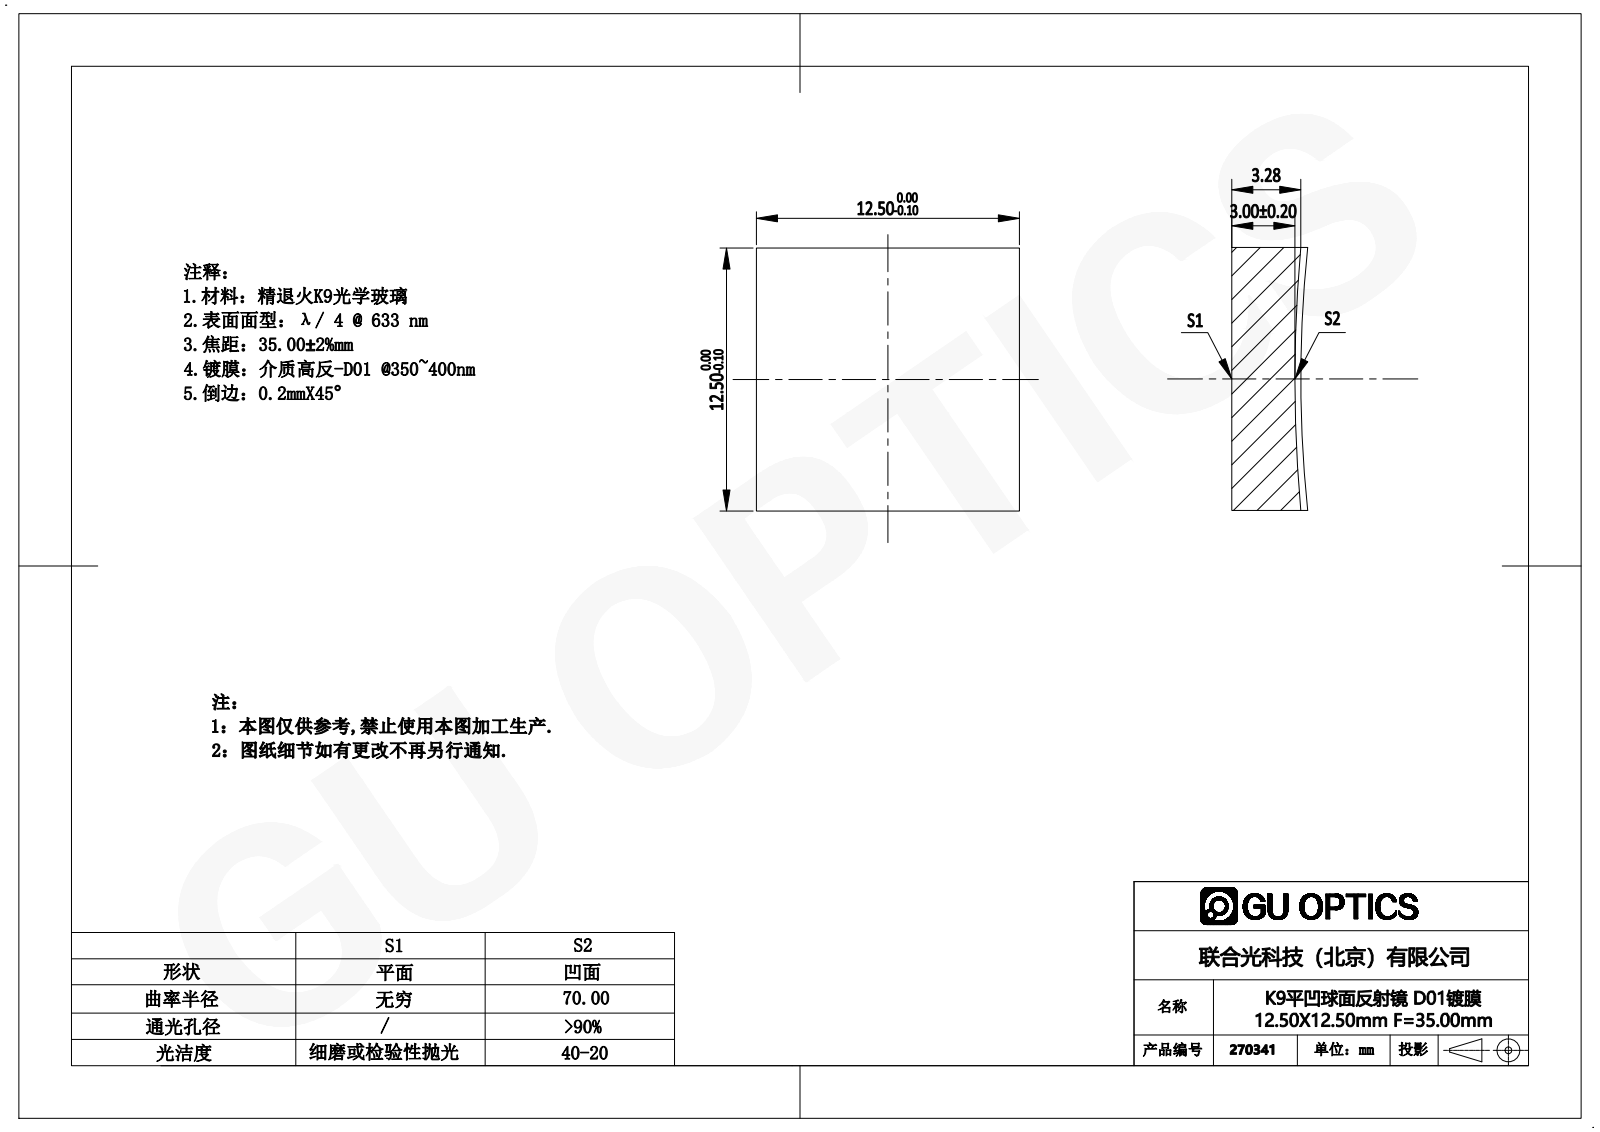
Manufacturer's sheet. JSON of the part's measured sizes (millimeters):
{"part_name": "270016", "step_written_by": "SolidWorks 2019 (AUTOMOTIVE_DESIGN)", "units": "millimeters", "bodies": {"solids": 1, "faces": 7, "planar": 5, "cylindrical": 0, "other": 2}, "overall_size": [12.5, 12.5, 3.56], "volume_mm3": 498, "surface_area_mm2": 482, "face_to_face_distances": [12.5]}
